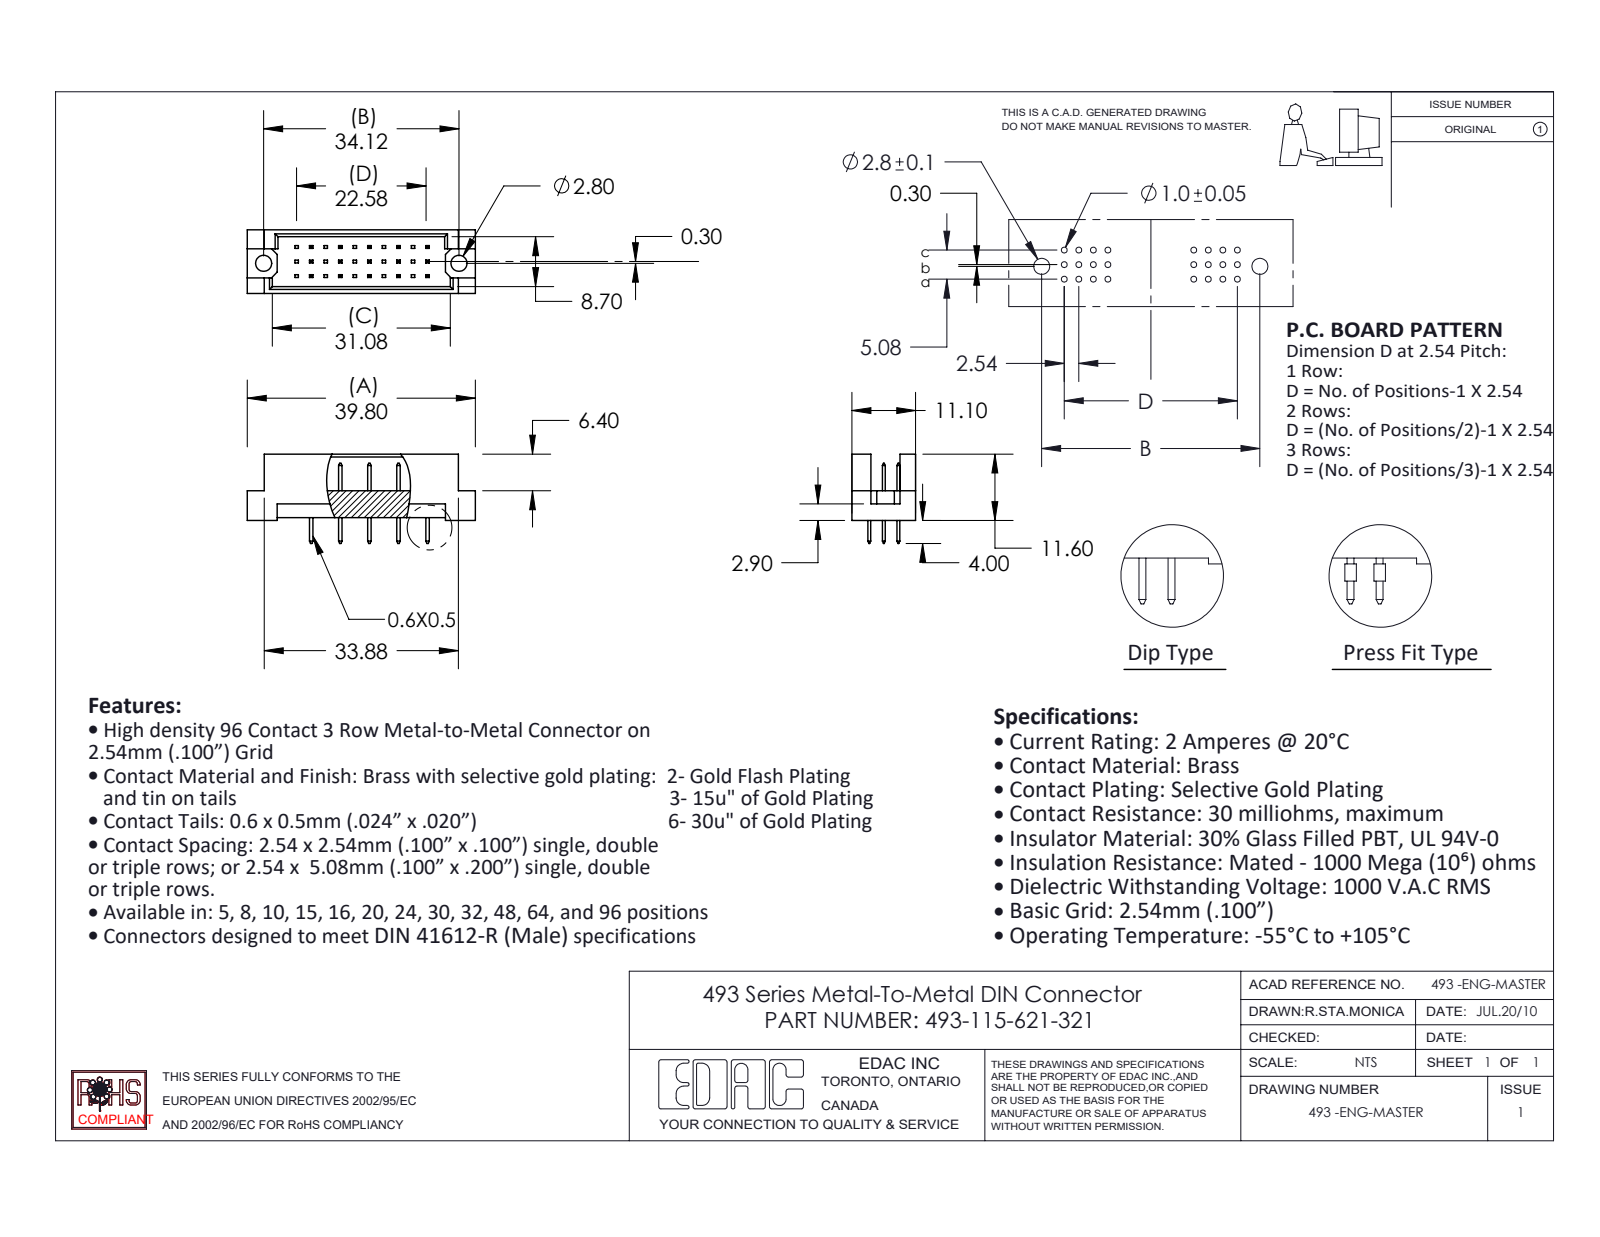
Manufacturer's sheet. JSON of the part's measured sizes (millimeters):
{"part_name": "493-290_21; 493-115-621-322; 493 Part_30", "step_written_by": "SolidWorks 2020 (CONFIG_CONTROL_DESIGN)", "units": "millimeters", "bodies": {"solids": 16, "faces": 382, "planar": 378, "cylindrical": 4, "other": 0}, "overall_size": [39.8, 15.6, 11.1], "volume_mm3": 2434, "surface_area_mm2": 3194, "round_holes": [[2.8, 2]], "face_to_face_distances": [1.2, 9.9, 11.1, 5.08, 0.5, 8.7, 2.54, 4.7, 10.16, 2.76], "hole_center_spacings": [34.12]}
